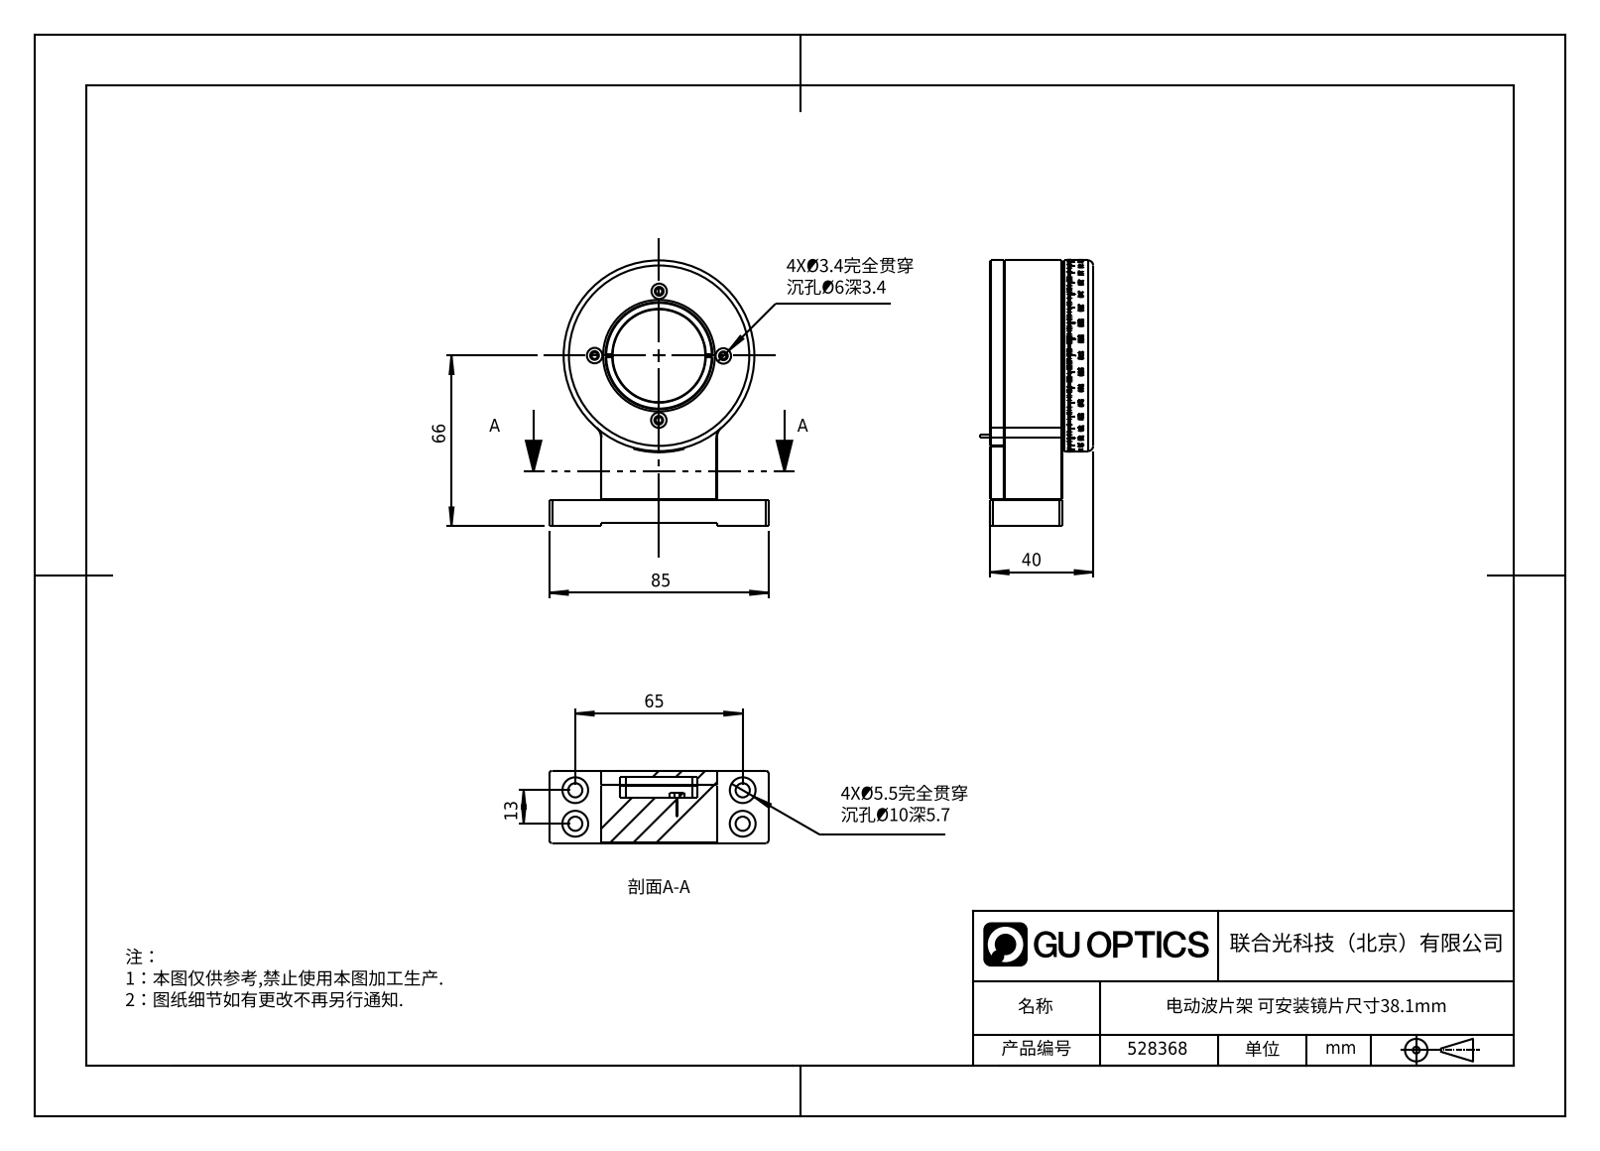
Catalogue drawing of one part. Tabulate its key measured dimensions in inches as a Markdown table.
| quantity | value |
| --- | --- |
| part name | 528368 |
| STEP written by | SolidWorks 2020 (CONFIG_CONTROL_DESIGN) |
| units | inches |
| bodies | 0 solids, 423 faces (250 planar, 129 cylindrical, 44 other) |
| overall size | 4.055 × 3.346 × 1.722 |
| round holes (diameter × count) | 0.049 × 16, 0.071 × 16, 0.138 × 12, 0.13 × 8, 0.098 × 5, 0.134 × 4, 0.177 × 4, 0.217 × 4, 0.236 × 4, 0.315 × 4, 0.394 × 4, 0.081 × 2 |
| round bosses / shafts (diameter × count) | 2.913 × 1, 2.598 × 1, 2.579 × 1, 0.118 × 1 |
| partial cylindrical surfaces (radius × count) | 0.079 × 8, 0.039 × 4, 0.004 × 2, 0.197 × 2, 1.467 × 1 |
| main face-to-face distances | 1.161, 1.102, 0.217, 0.039, 0.413, 0.02, 0.059, 1.358, 0.925, 0.945 |
| hole center spacings | 1.378, 1.22, 1.306, 2.252, 0.984, 1.392, 1.969, 0.157 |
